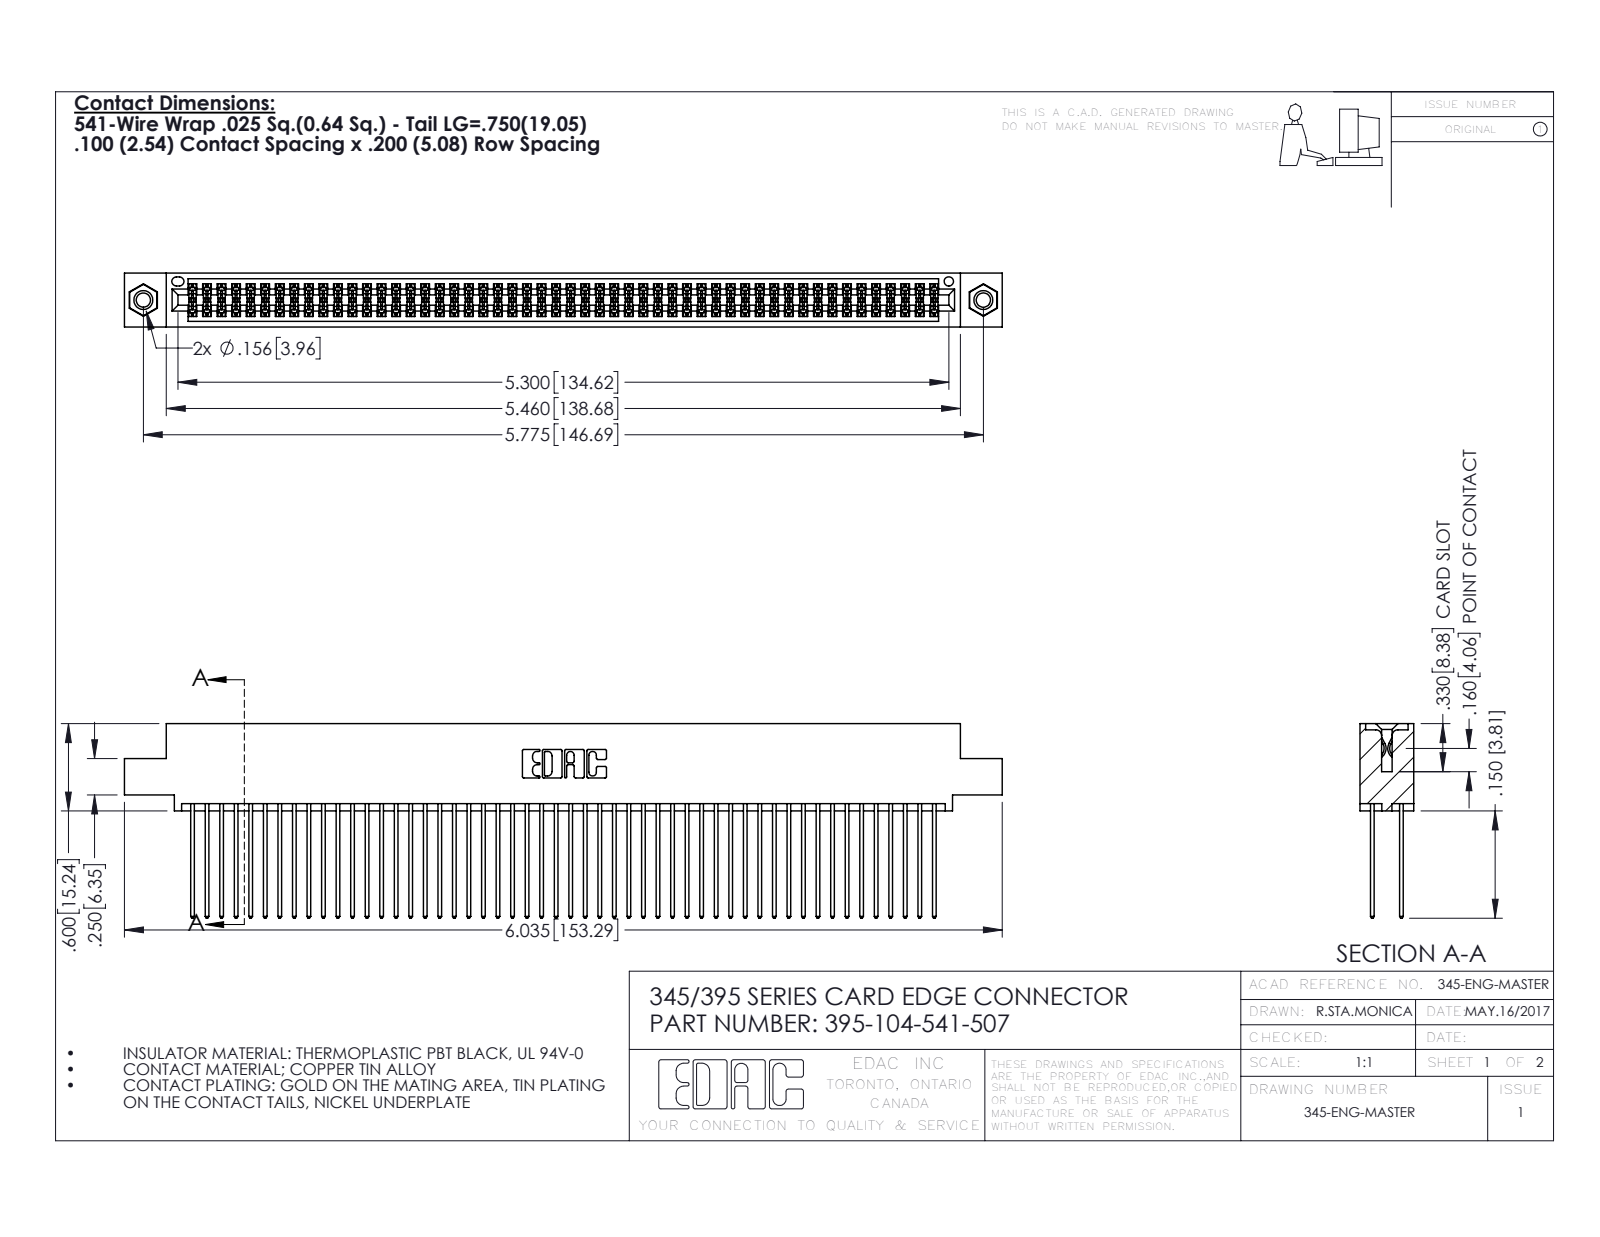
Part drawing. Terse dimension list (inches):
name: 395-104-541-507; 345-250-001_345-250-005-103; 345 Part_0.110 Offset - 0.156 Dia-TI; 345-292-001_345-293-141
written by: SolidWorks 2016 (CONFIG_CONTROL_DESIGN)
unit: in
bodies: 107 solids, 5390 faces (3548 planar, 1826 cylindrical, 16 other)
size: 6.035 × 1.337 × 0.37
volume: 0.945 in³; area: 40.33 in²
holes: 2× ⌀0.098, 2× ⌀0.125, 2× ⌀0.156, 1× ⌀0.064
bosses: 2× ⌀0.155
rounds: 156× R0.006, 104× R0.01, 22× R0.01, 6× R0.007, 6× R0.031, 3× R0.026, 2× R0.014, 2× R0.019
face distances: 0.072, 0.298, 0.2, 0.098, 0.272, 0.025, 0.225, 0.37, 0.175, 0.149
hole spacings: 0.27, 5.539, 5.775
